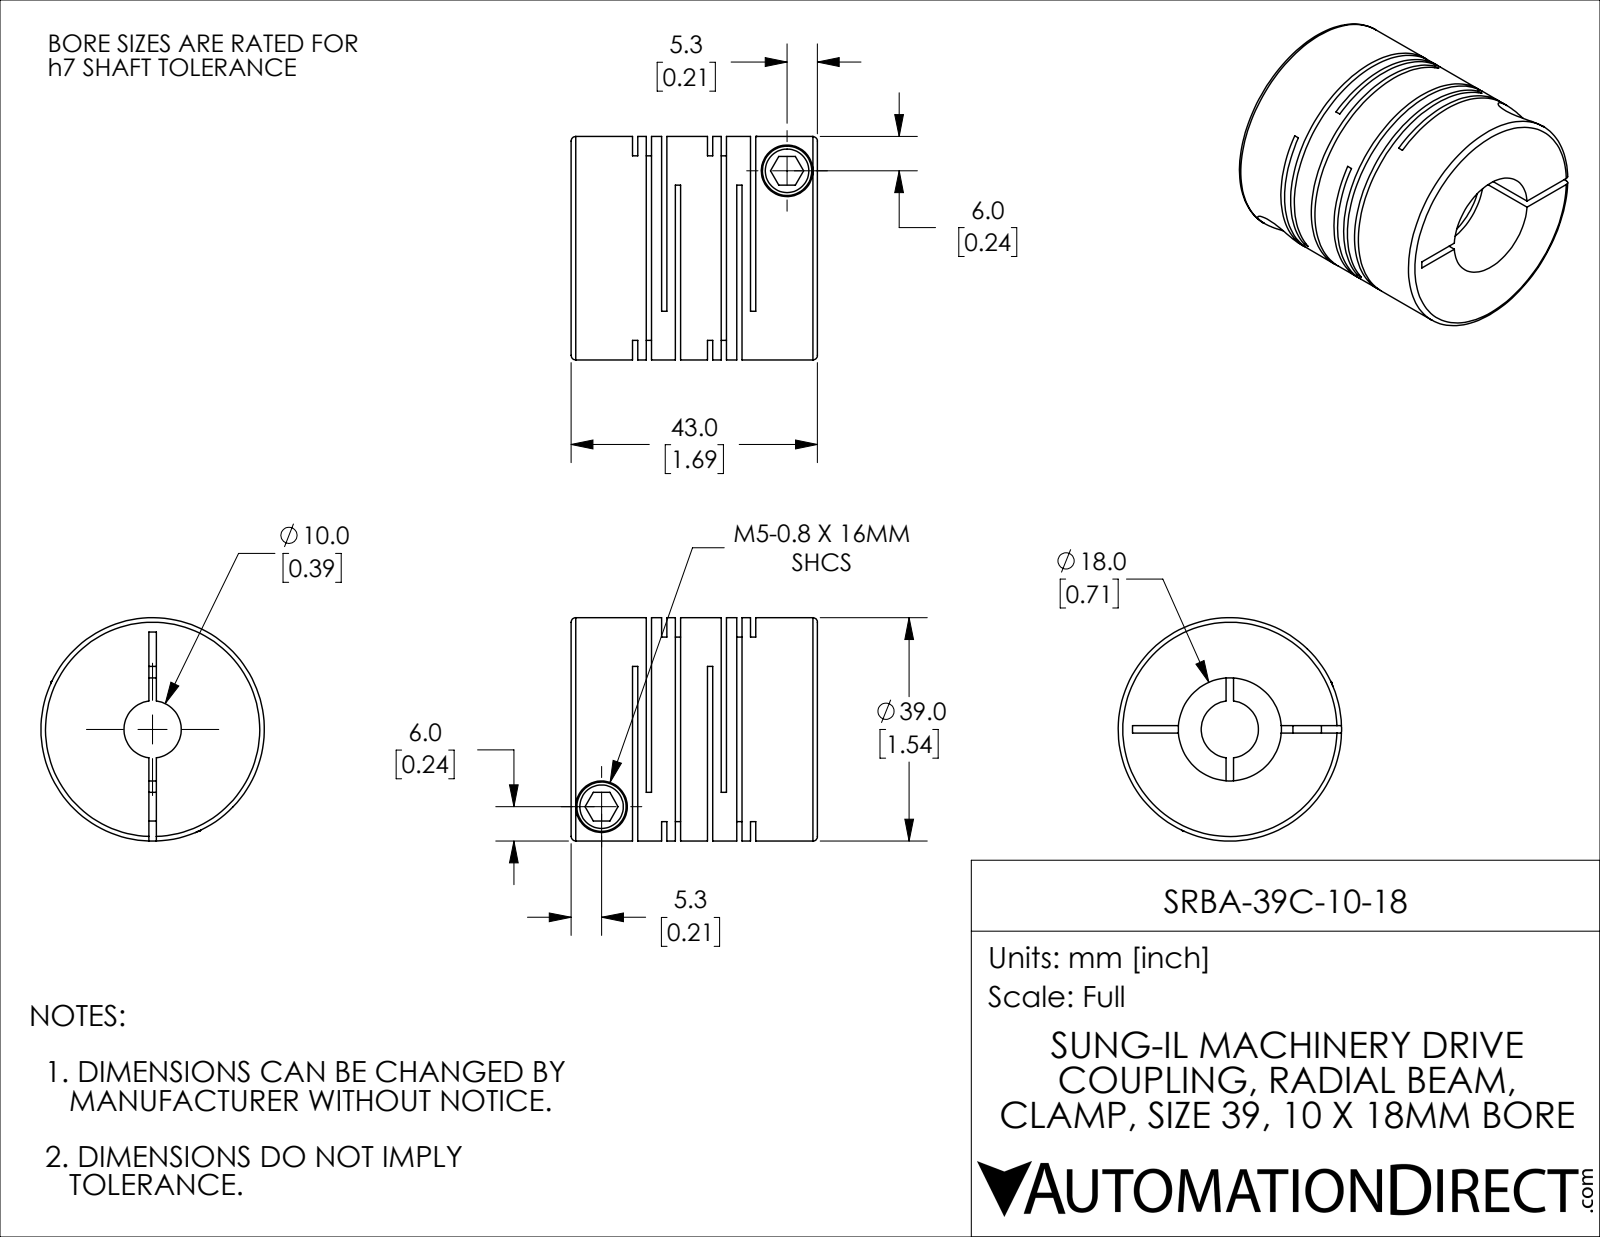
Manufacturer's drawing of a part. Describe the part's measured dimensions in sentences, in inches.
The part is named "SRBA-39C-10-18". Its 3-D file was written by "SolidWorks 2021 (CONFIG_CONTROL_DESIGN)". It is 1 solid with 114 faces: 60 planar, 42 cylindrical and 12 other. Overall it measures 1.693 by 1.535 by 1.535 inches. Its volume is 2.152 cubic inches and its surface area 34.66 square inches. Round holes: 2 of diameter 0.197, 2 of diameter 0.354, 1 of diameter 0.394, 1 of diameter 0.709. Round bosses or shafts: 2 of diameter 0.339, 1 of diameter 1.535. The main face-to-face distances are 0.516, 0.036, 0.094, 0.201, 0.421, 0.552, 0.717, 0.131, 0.058, 0.61.
